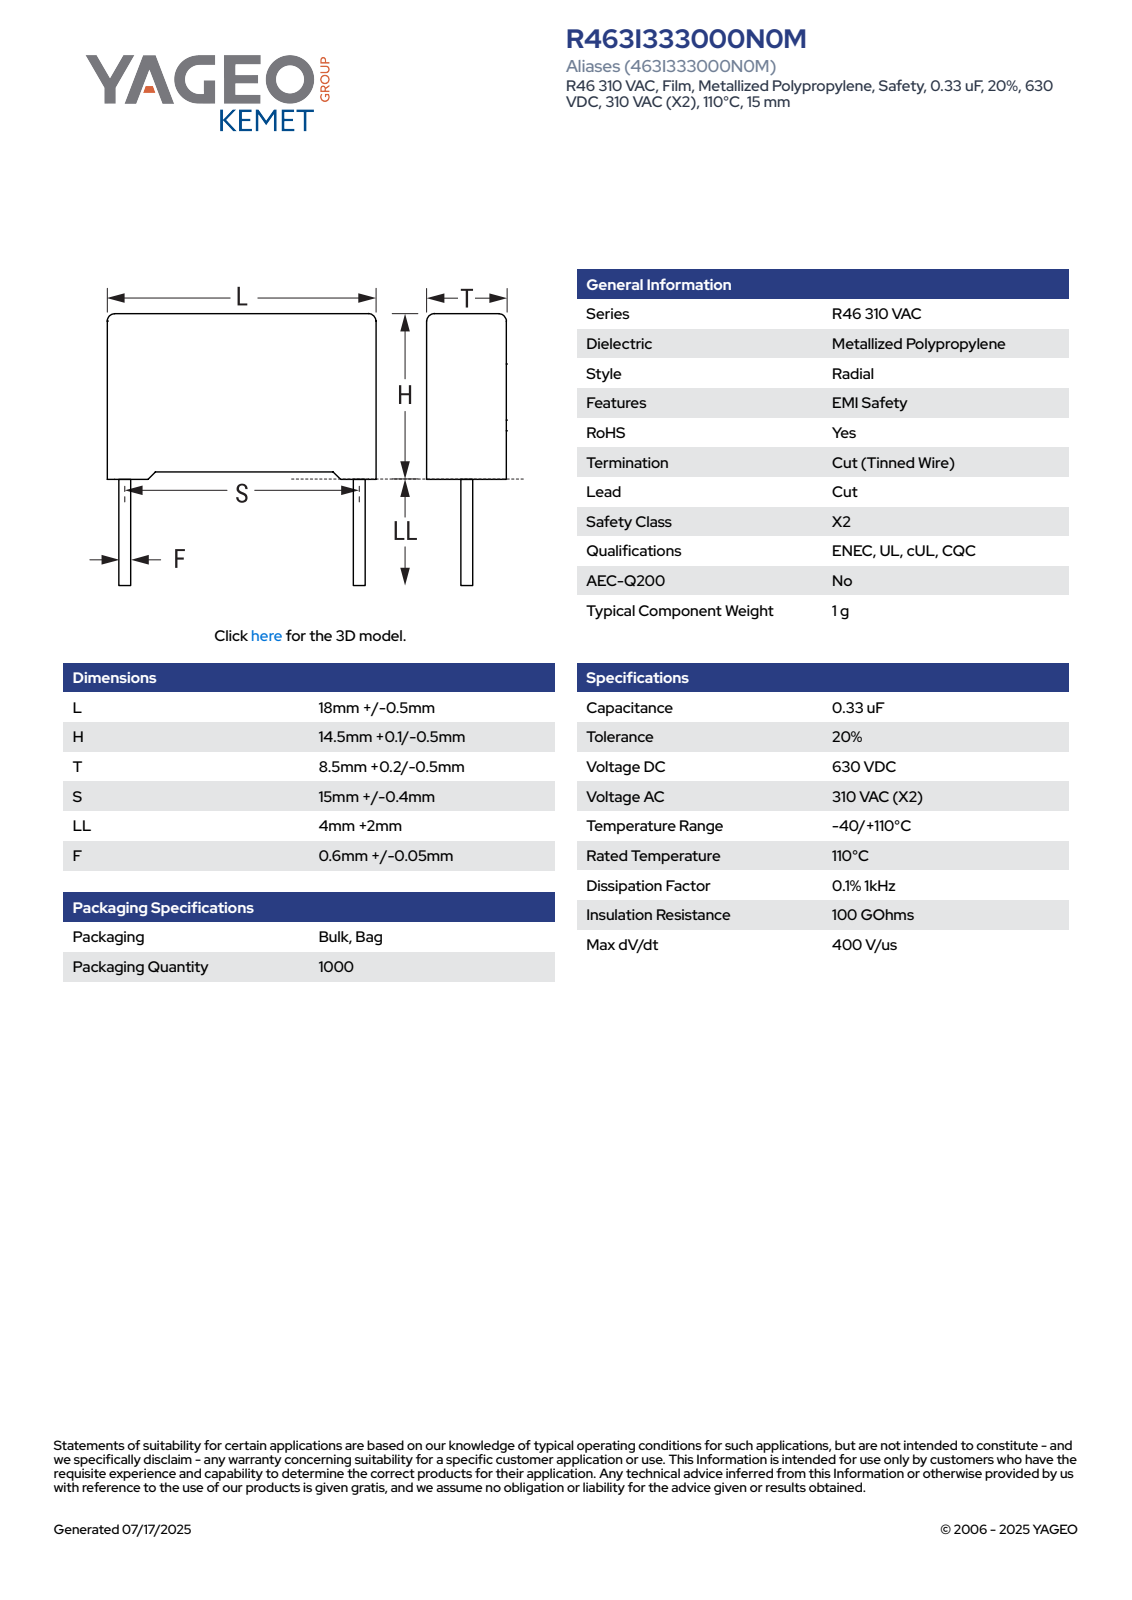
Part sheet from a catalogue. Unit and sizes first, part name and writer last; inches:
Units: inches
Overall size (bounding box): 0.811 × 0.728 × 0.343
Round bosses / shafts (diameter × count): ⌀0.026 ×2
Partial cylindrical surfaces — rounded edges, fillets, slot ends (radius × count): R0.02 ×4
Main face-to-face distances: 0.343, 0.545, 0.728, 0.024, 0.03, 0.575, 0.318, 0.02, 0.555, 0.704
Volume: 0.137 in³ · Surface area: 1.817 in²
Bodies: 4 solids, 85 faces (77 planar, 8 cylindrical, 0 other)
Part name (STEP PRODUCT): CFR_RB2_18X14.5X8.5_L18.5H14.6T8.7S15LL6F0.65
STEP written by: SolidWorks 2021 (AUTOMOTIVE_DESIGN)
